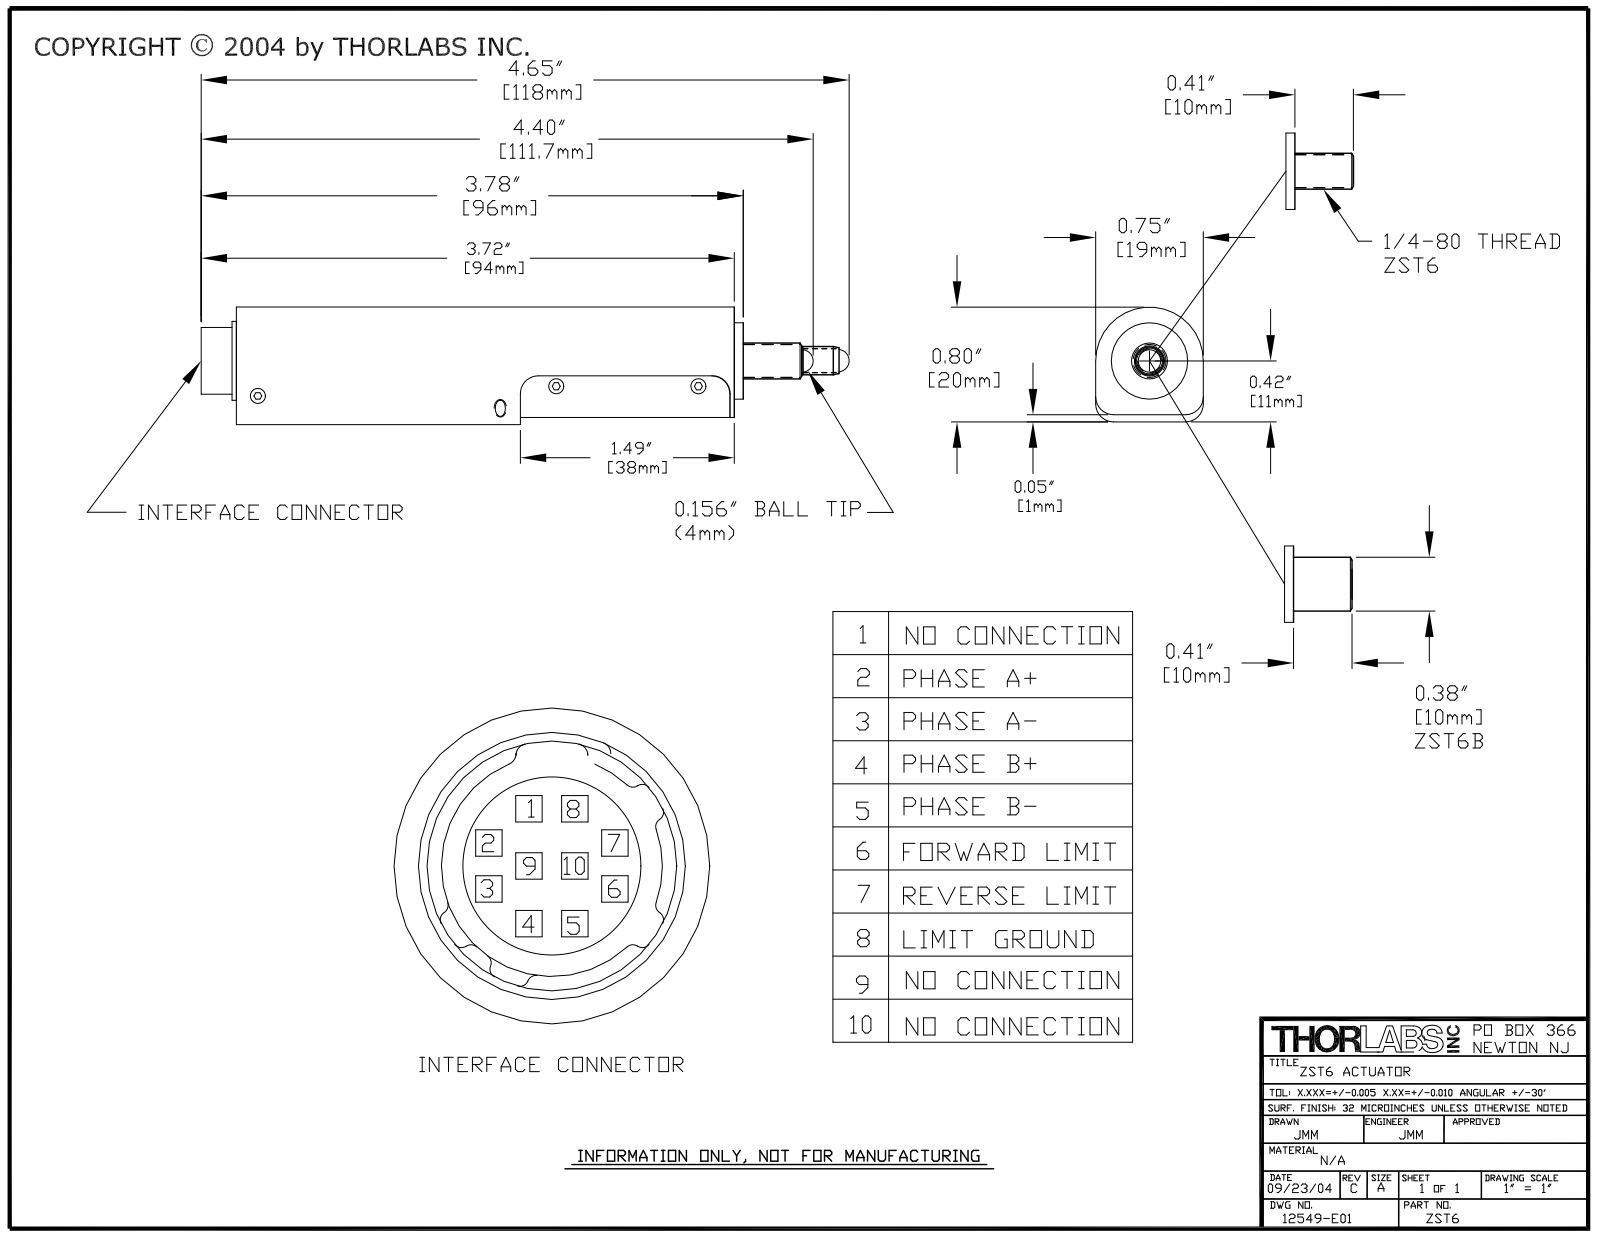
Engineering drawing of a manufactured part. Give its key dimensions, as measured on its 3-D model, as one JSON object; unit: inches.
{"part_name": "12549-E0W", "step_written_by": "SolidWorks 2007 (AUTOMOTIVE_DESIGN)", "units": "inches", "bodies": {"solids": 0, "faces": 512, "planar": 133, "cylindrical": 326, "other": 53}, "overall_size": [4.702, 0.828, 0.82], "round_holes": [[0.045, 7], [0.045, 3], [0.086, 2], [0.14, 2], [0.156, 1], [0.386, 1]], "round_bosses_or_shafts": [[0.139, 4], [0.073, 2], [0.63, 1], [0.551, 1], [0.464, 1], [0.3, 1], [0.25, 1], [0.23, 1]], "partial_cylinders_radius": [[0.125, 8], [0.03, 3], [0.345, 1], [0.375, 1]], "face_to_face_distances": [0.75, 0.05, 0.03, 3.44, 3.47, 3.535, 3.505, 0.065, 0.26, 0.29], "hole_center_spacings": [0.071, 0.14, 0.1, 0.103, 0.108, 0.128, 0.158, 0.199]}
